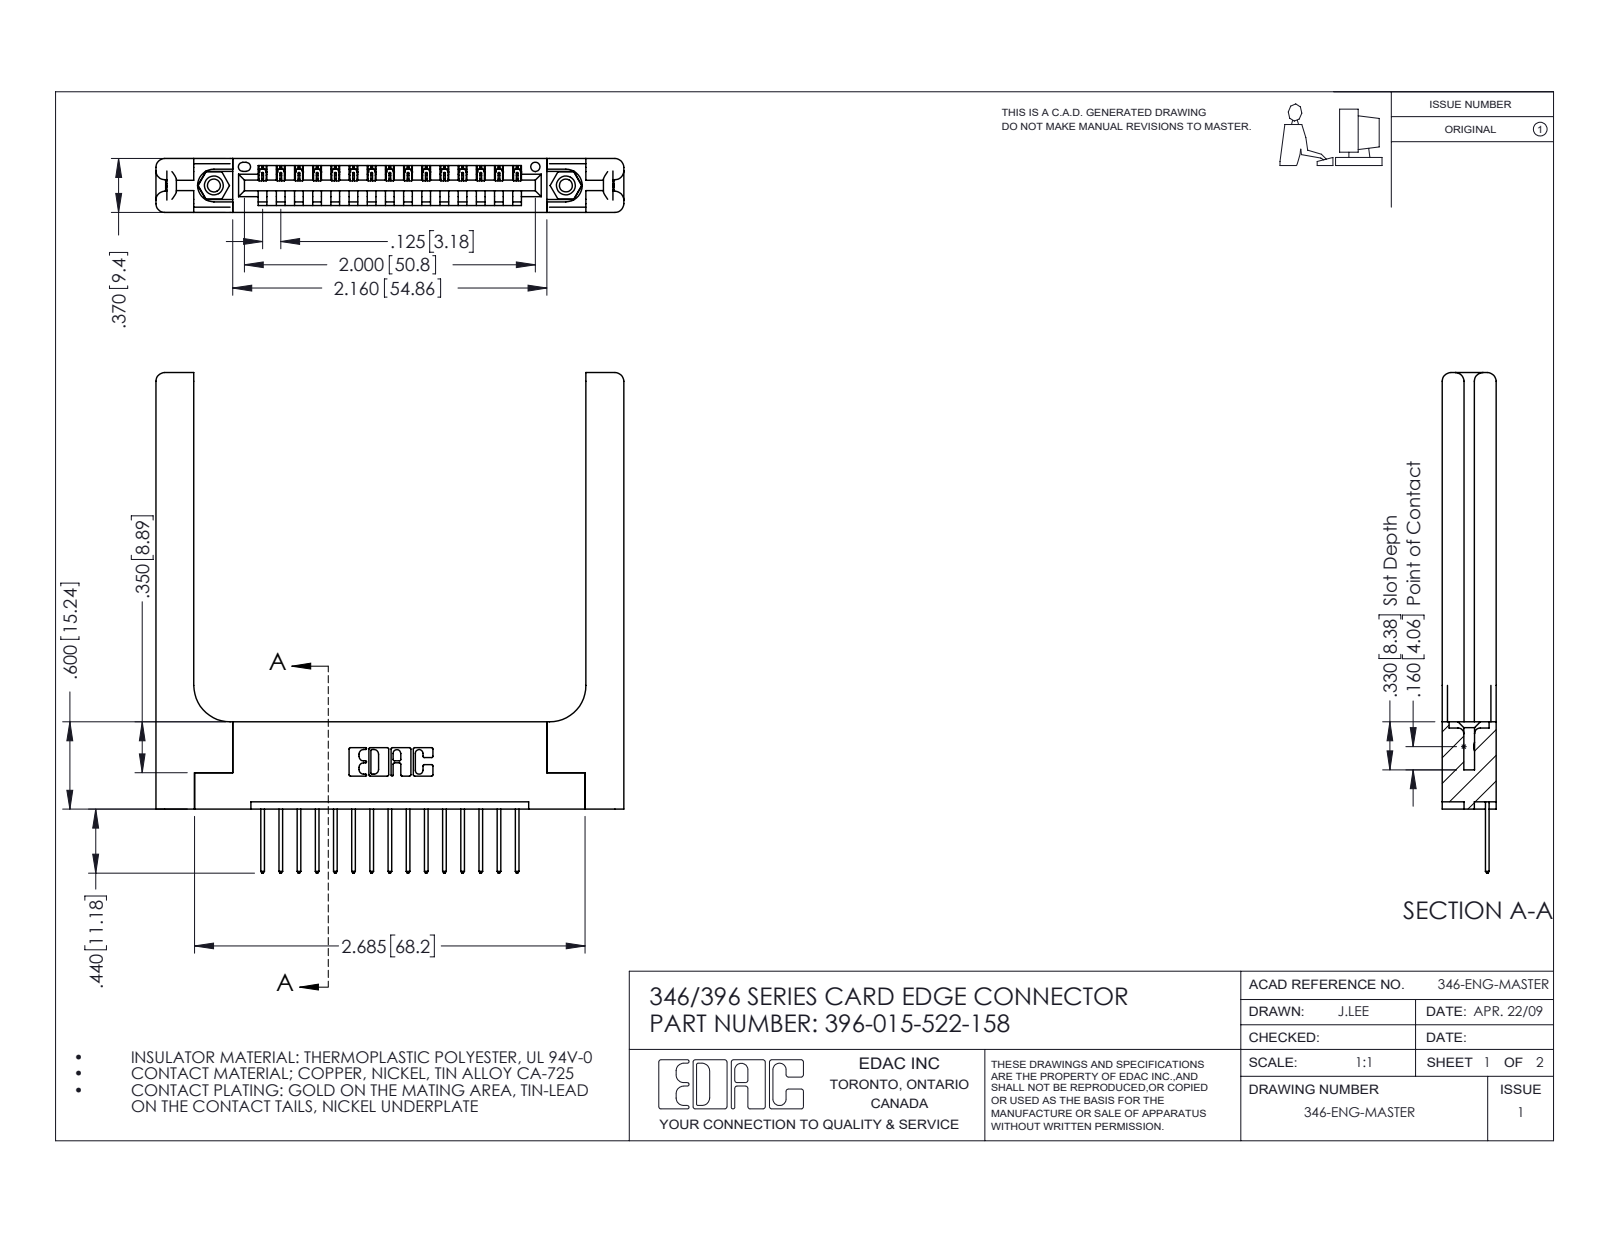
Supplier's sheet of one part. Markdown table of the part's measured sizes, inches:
| quantity | value |
| --- | --- |
| part name | 345-292-001_345-293-122; 346 Part_Flush Mounting Lugs - 0.156 Dia-TH; 345-250-001_345-250-001-102; 346-220-058_345-220-058 (+1 more) |
| STEP written by | SolidWorks 2016 (CONFIG_CONTROL_DESIGN) |
| units | inches |
| bodies | 20 solids, 1248 faces (824 planar, 364 cylindrical, 60 other) |
| overall size | 3.44 × 3.216 × 0.37 |
| volume | 0.925 in³ |
| surface area | 22.44 in² |
| round holes (diameter × count) | 0.089 × 2, 0.125 × 2, 0.156 × 2, 0.064 × 1 |
| round bosses / shafts (diameter × count) | 0.155 × 2 |
| partial cylindrical surfaces (radius × count) | 0.006 × 30, 0.01 × 30, 0.01 × 22, 0.06 × 16, 0.007 × 6, 0.031 × 6, 0.026 × 3, 0.03 × 2 |
| main face-to-face distances | 0.37, 0.15, 0.072, 0.148, 0.048, 0.322, 0.25, 0.22, 0.102, 0.173 |
| hole center spacings | 0.246, 2.213, 2.42 |
